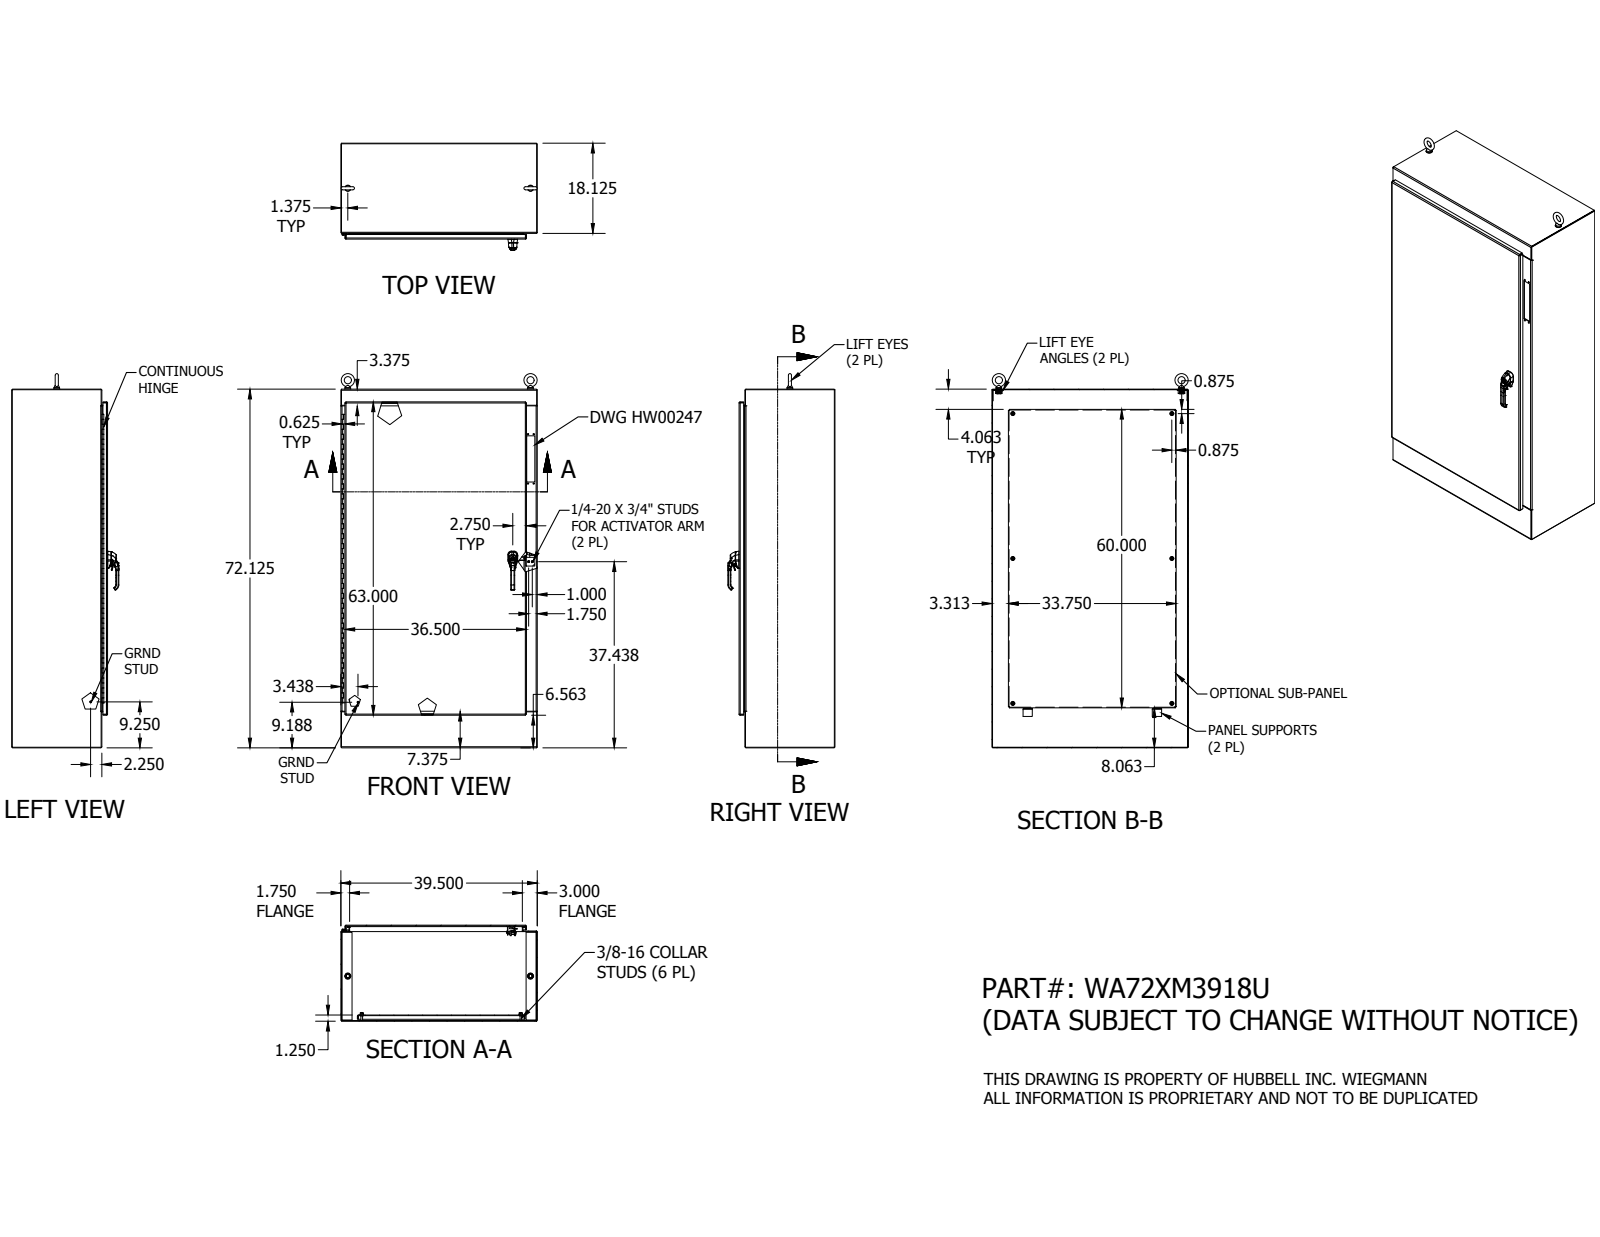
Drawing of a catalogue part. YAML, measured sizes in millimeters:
part_name: "WA72XM39U_BACK; WA72XM18U_RIGHT_SIDE; WA72XM18U_LEFT_SIDE; WAXM3918U_TOP_ENDWALL (+8 more)"
step_written_by: "Autodesk Inventor 2014 (AUTOMOTIVE_DESIGN)"
units: millimeters
bodies: {solids: 103, faces: 3698, planar: 1615, cylindrical: 1232, other: 851}
overall_size: [1911.29, 1003.3, 547.14]
volume: 26160000
surface_area: 16740000
round_holes:
  - {diameter: 9.52, count: 10}
  - {diameter: 7.02, count: 8}
  - {diameter: 7.14, count: 7}
  - {diameter: 3.96, count: 6}
  - {diameter: 6.35, count: 6}
  - {diameter: 7.8, count: 6}
  - {diameter: 14.29, count: 6}
  - {diameter: 5.08, count: 4}
  - {diameter: 7.37, count: 4}
  - {diameter: 5.4, count: 3}
  - {diameter: 3, count: 2}
  - {diameter: 3.17, count: 2}
round_bosses_or_shafts:
  - {diameter: 15.88, count: 10}
  - {diameter: 8.38, count: 9}
  - {diameter: 14.29, count: 6}
  - {diameter: 9.52, count: 4}
  - {diameter: 8.56, count: 4}
  - {diameter: 6.35, count: 4}
  - {diameter: 6, count: 3}
  - {diameter: 31.75, count: 2}
partial_cylinders:
  - {radius: 0.5, count: 187}
  - {radius: 0.3, count: 109}
  - {radius: 0.51, count: 48}
  - {radius: 0.47, count: 21}
  - {radius: 2.38, count: 21}
  - {radius: 5.56, count: 20}
  - {radius: 1.27, count: 14}
  - {radius: 2, count: 14}
face_to_face_distances: [3.17, 3.18, 28.58, 486.84, 483.67, 490.02, 486.85, 31.75, 455.09, 458.27]
hole_center_spacings: [1099.05, 771.85, 812.8, 9.67, 9.69, 9.72, 19.05, 19.36]
